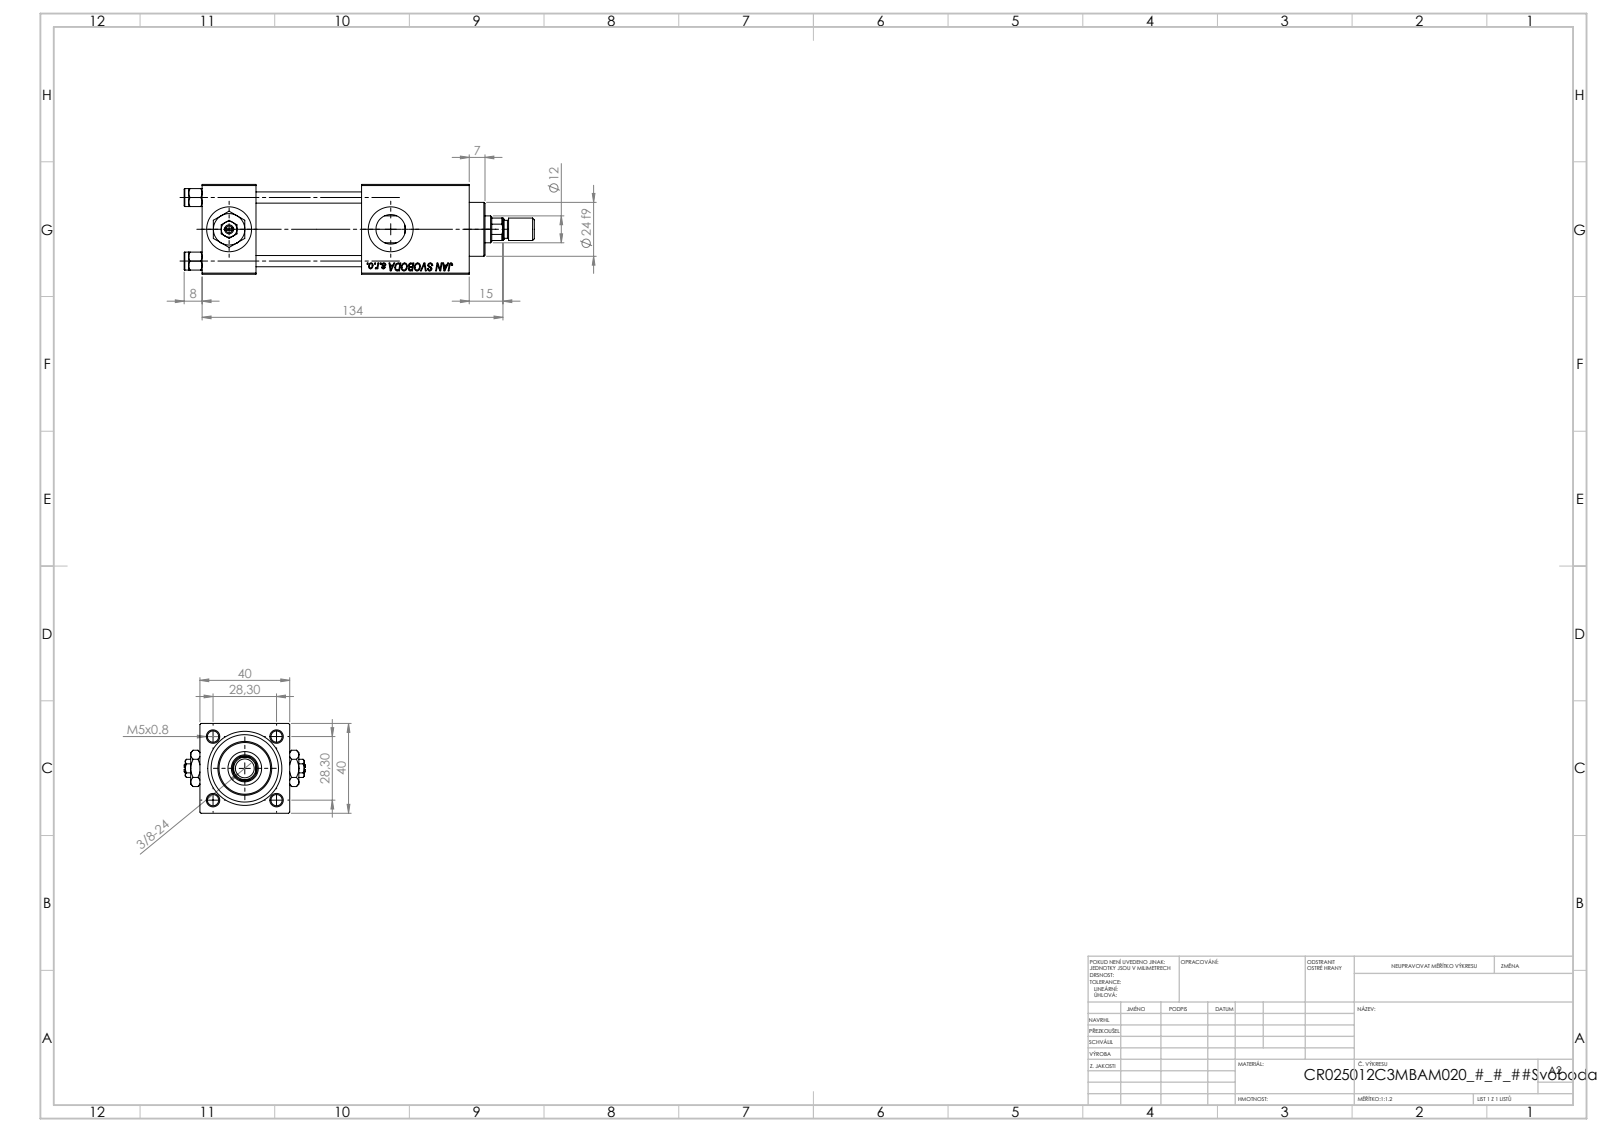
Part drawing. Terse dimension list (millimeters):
name: V215_VC_A; V215CR_C_TYCINKA; V215CR_C_Body; NUT_M5_C (+3 more)
written by: SolidWorks 2019 (CONFIG_CONTROL_DESIGN)
unit: mm
bodies: 14 solids, 1262 faces (576 planar, 102 cylindrical, 584 other)
size: 156 × 54 × 40
volume: 142 017 mm³; area: 56 820 mm²
holes: 4× ⌀5, 3× ⌀20, 2× ⌀7, 2× ⌀13.16, 1× ⌀6.5, 1× ⌀12, 1× ⌀15, 1× ⌀25, 1× ⌀30
bosses: 5× ⌀8, 1× ⌀31, 1× ⌀24, 1× ⌀10
rounds: 1× R5.5
face distances: 40, 24, 39.8, 48, 90.3, 66.3, 71, 47, 19.3, 119
hole spacings: 20.01, 28.3, 40.02, 72
